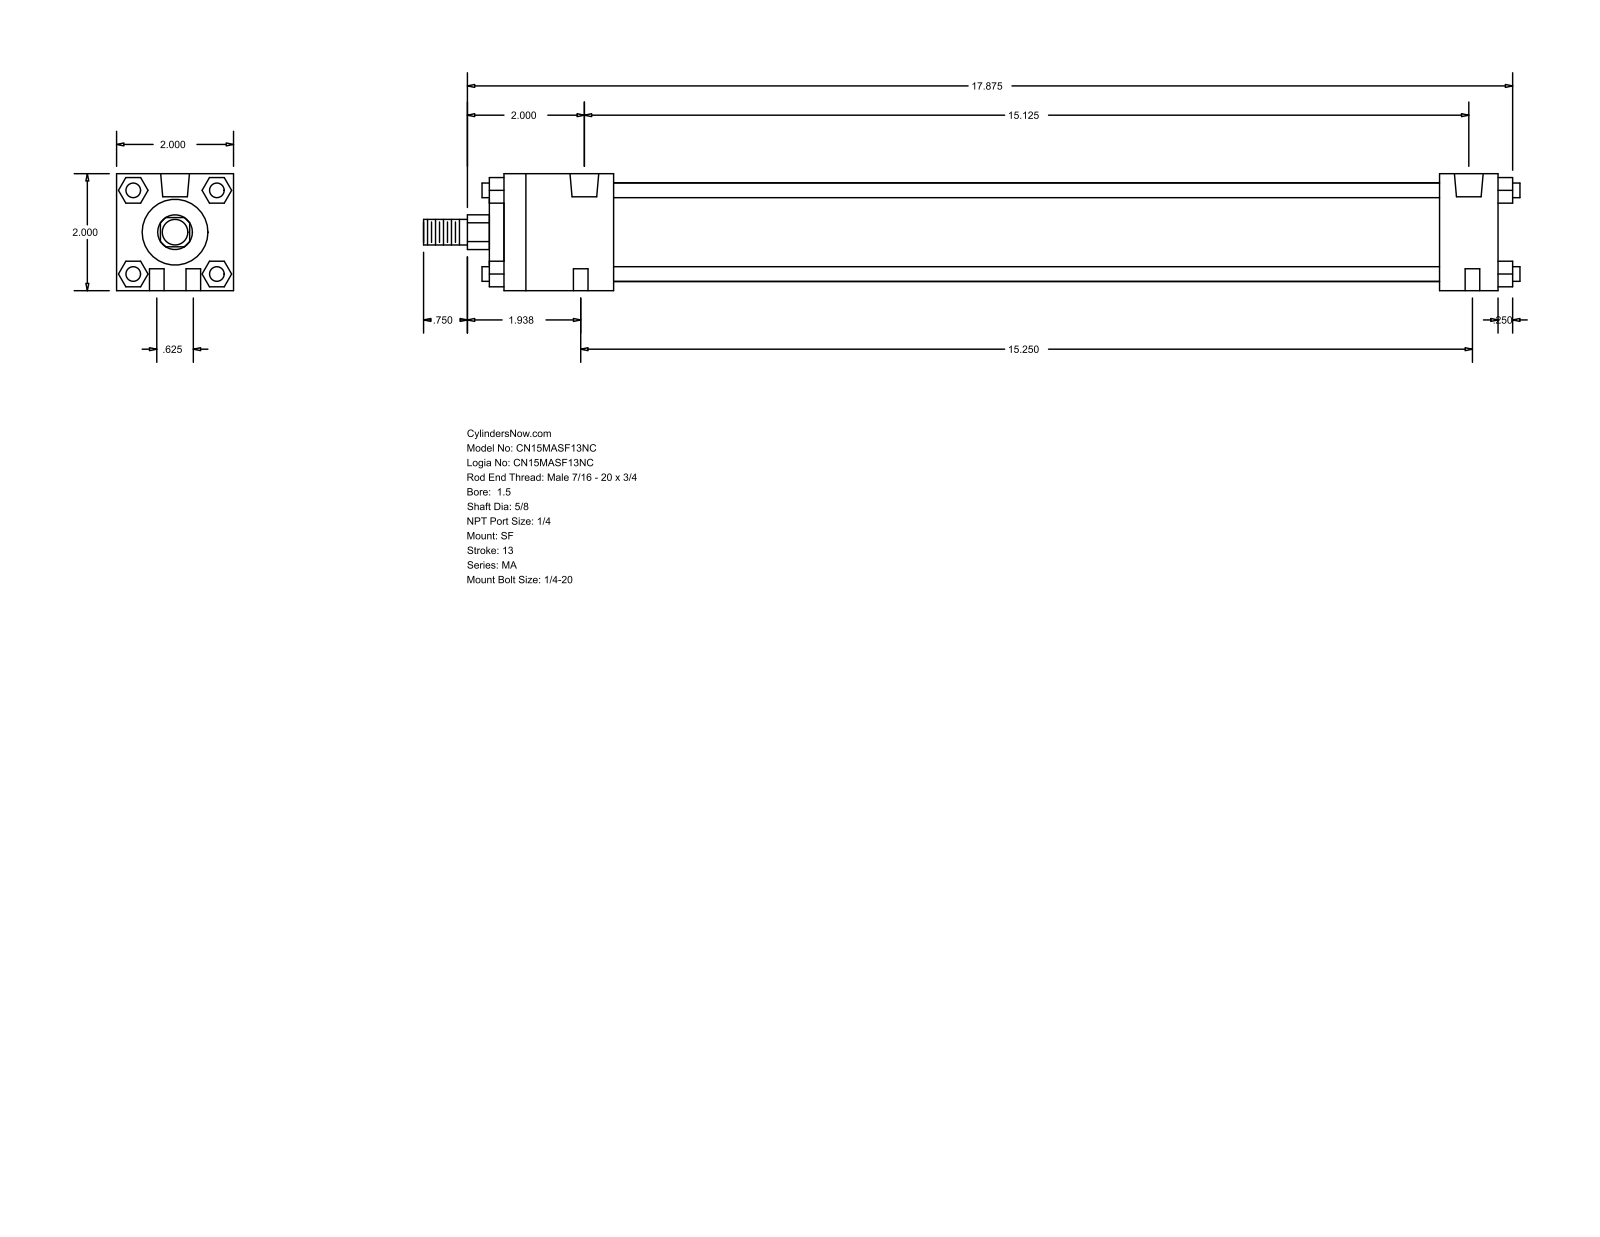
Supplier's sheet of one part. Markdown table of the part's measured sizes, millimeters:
| quantity | value |
| --- | --- |
| part name | MA_SF__0150_0.625 |
| STEP written by | GSSL Pune (CONFIG_CONTROL_DESIGN) |
| units | millimeters |
| bodies | 0 solids, 124 faces (94 planar, 30 cylindrical, 0 other) |
| overall size | 476.25 × 50.8 × 50.8 |
| round holes (diameter × count) | 6.35 × 4, 7.94 × 2, 12.49 × 2 |
| round bosses / shafts (diameter × count) | 6.35 × 4, 42.93 × 1, 28.57 × 1, 15.88 × 1, 11.11 × 1 |
| partial cylindrical surfaces (radius × count) | 7.54 × 1 |
| main face-to-face distances | 50.8, 431.8, 47.62, 406.39, 358.77, 384.18, 25.41, 6.35, 53.97, 412.74 |
| hole center spacings | 8.1, 15.88, 384.18, 385.84, 385.85, 387.35, 387.68 |
